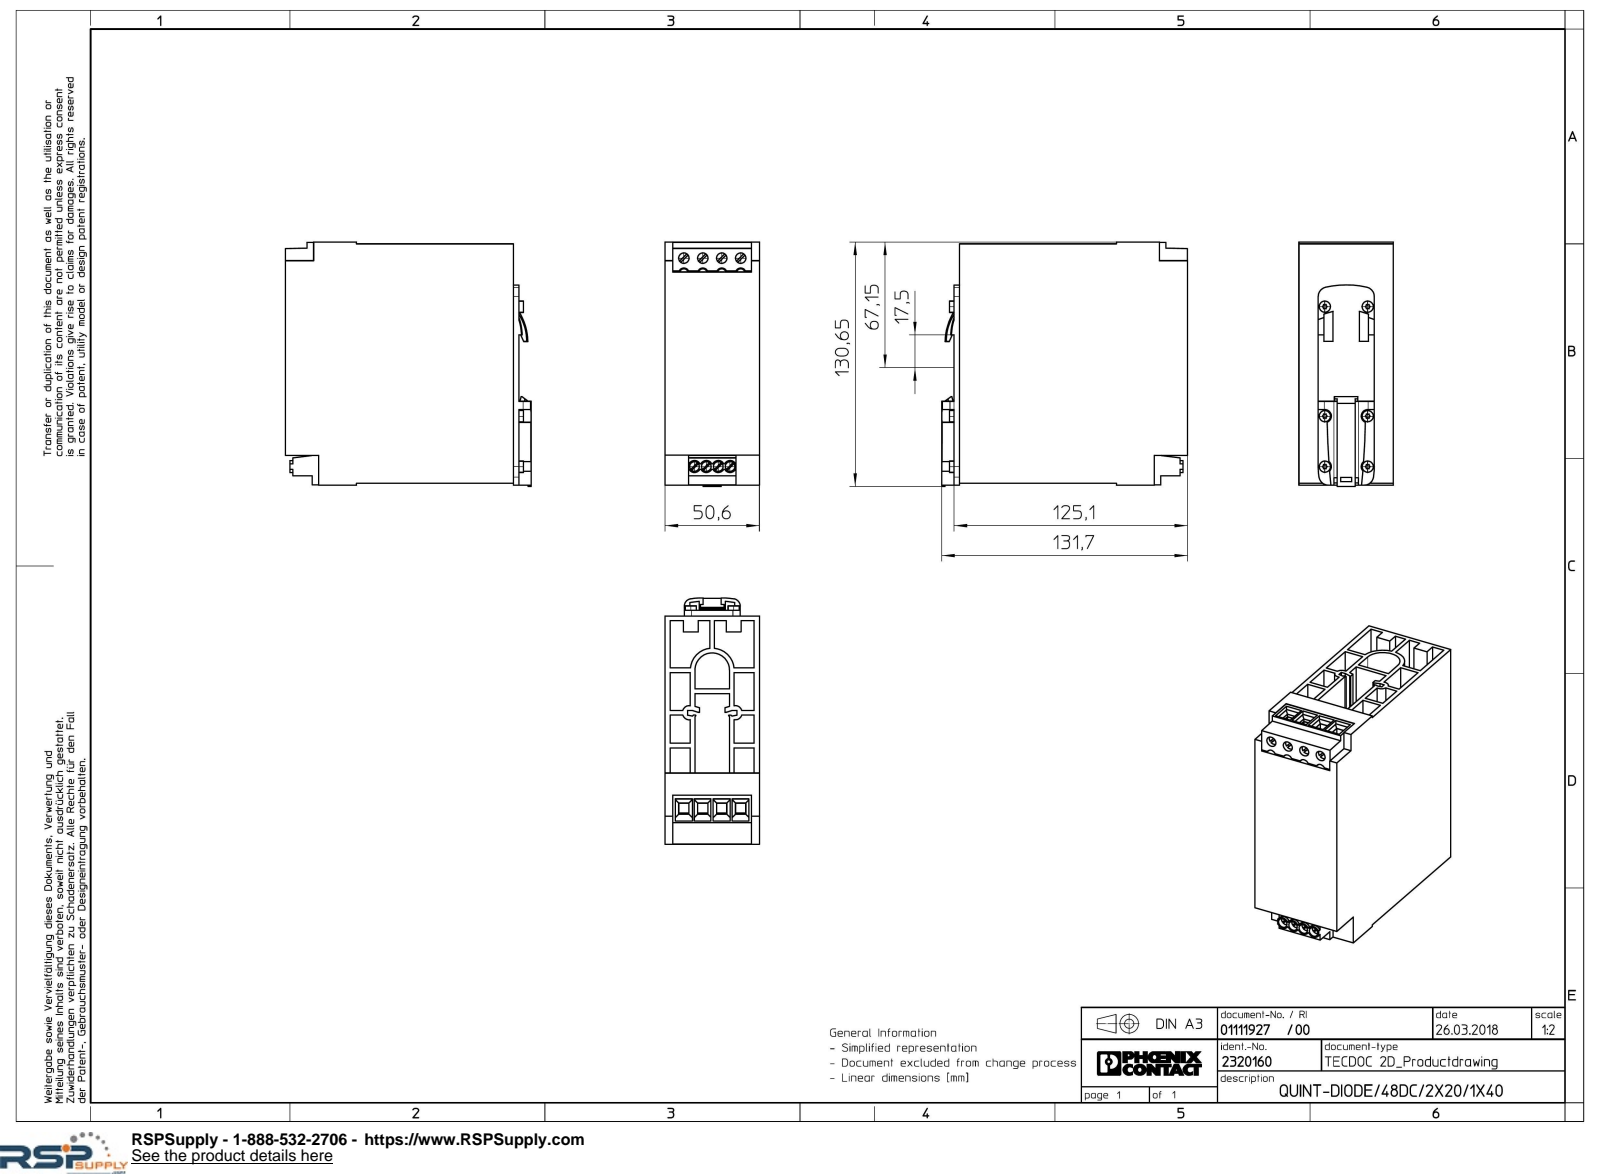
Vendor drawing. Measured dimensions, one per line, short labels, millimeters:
name: QUINT_DIODE_48DC_2X20_1X40-select
written by: Creo Elements/Direct Modeling 18.1I 14-Aug-2016 (C) Parametric Technology GmbH (AUTOMOTIVE_DESIGN)
unit: mm
bodies: 1 solid, 502 faces (370 planar, 124 cylindrical, 8 other)
size: 131.7 × 130.65 × 50.6
volume: 415 502 mm³; area: 151 624 mm²
holes: 4× ⌀5.2, 4× ⌀5.6
bosses: 6× ⌀6
rounds: 36× R1.3, 16× R2.7, 8× R3.5, 4× R0.5, 4× R2.75, 4× R3.25, 4× R5, 2× R0.25
face distances: 2.5, 2.8, 47.8, 50.6, 16.05, 34.55, 13.25, 31.75, 45, 13.55
hole spacings: 6.35, 10.16, 12.7, 20.32, 111.45, 111.52, 111.58, 112.08
